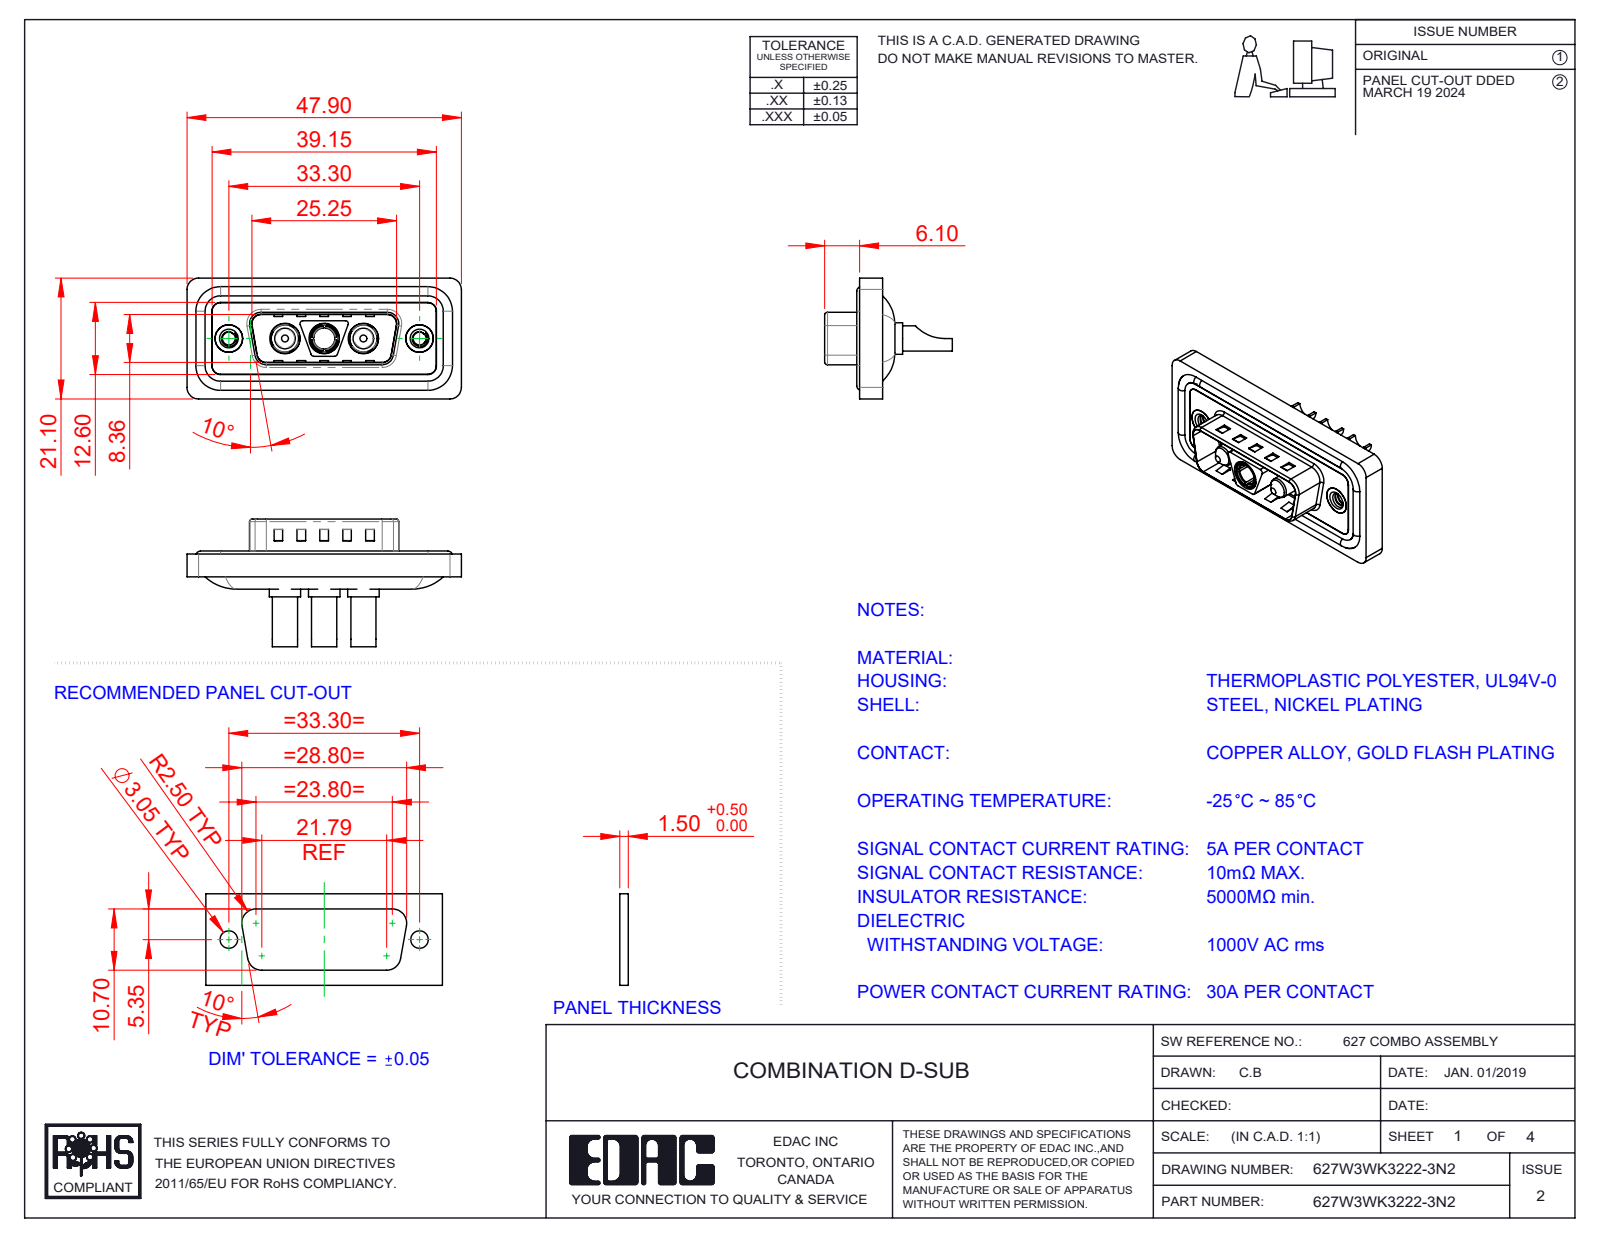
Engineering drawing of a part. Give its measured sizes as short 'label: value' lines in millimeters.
name: Power Socket_30A SC; 627W3WK3222-3N2; 627Combo Shell Rear_15 Contacts; 627Combo Shell Front_15 Contacts (+4 more)
written by: SolidWorks 2023 (CONFIG_CONTROL_DESIGN)
unit: mm
bodies: 13 solids, 627 faces (240 planar, 259 cylindrical, 128 other)
size: 47.9 × 22.3 × 21.1
volume: 5 760 mm³; area: 9 450 mm²
holes: 3× ⌀3.5, 3× ⌀4.85, 3× ⌀5.3, 2× ⌀2.26, 2× ⌀4, 2× ⌀4.8, 2× ⌀5, 1× ⌀3.7
bosses: 4× ⌀1.6, 3× ⌀5.5, 3× ⌀5.2, 3× ⌀4.75, 3× ⌀4.4, 3× ⌀3.75, 2× ⌀4.9, 2× ⌀3.6
rounds: 26× R1.5, 20× R2, 12× R0.5, 8× R1.6, 4× R0.25, 4× R0.6, 4× R0.65, 4× R0.9
face distances: 0.4, 1.1, 0.5, 1.6, 3.1, 1.5, 2.9, 0.82, 9.58, 2.5
hole spacings: 6.85, 9.8, 16.65, 23.5, 13.7, 33.3
